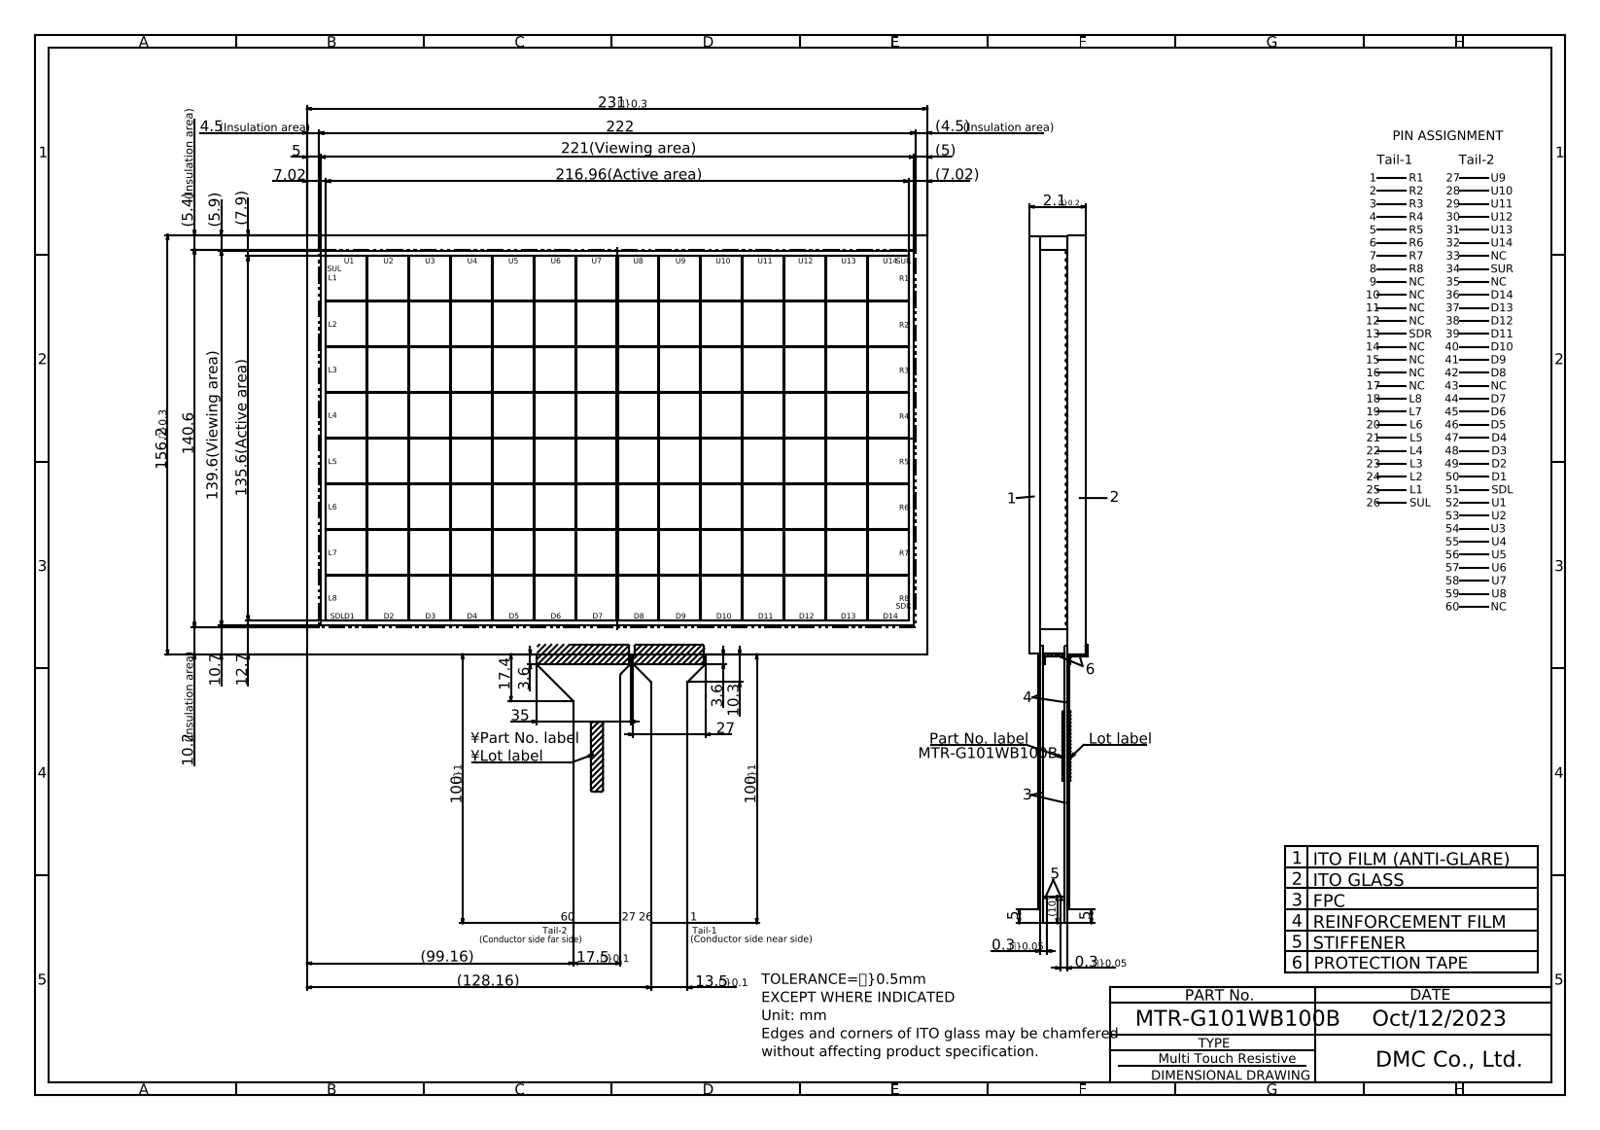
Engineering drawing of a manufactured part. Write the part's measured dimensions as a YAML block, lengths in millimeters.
part_name: "MTR-G101WB100B"
step_written_by: "Autodesk Inventor 2020 (CONFIG_CONTROL_DESIGN)"
units: millimeters
bodies: {solids: 1, faces: 294, planar: 282, cylindrical: 12, other: 0}
overall_size: [323.4, 287.44, 2.2]
volume: 76042
surface_area: 80729
partial_cylinders:
  - {radius: 1, count: 8}
  - {radius: 0.2, count: 4}
face_to_face_distances: [2.1, 1.8, 1.9, 2, 156.2, 231, 0.4, 2.2, 0.5, 0.7]
